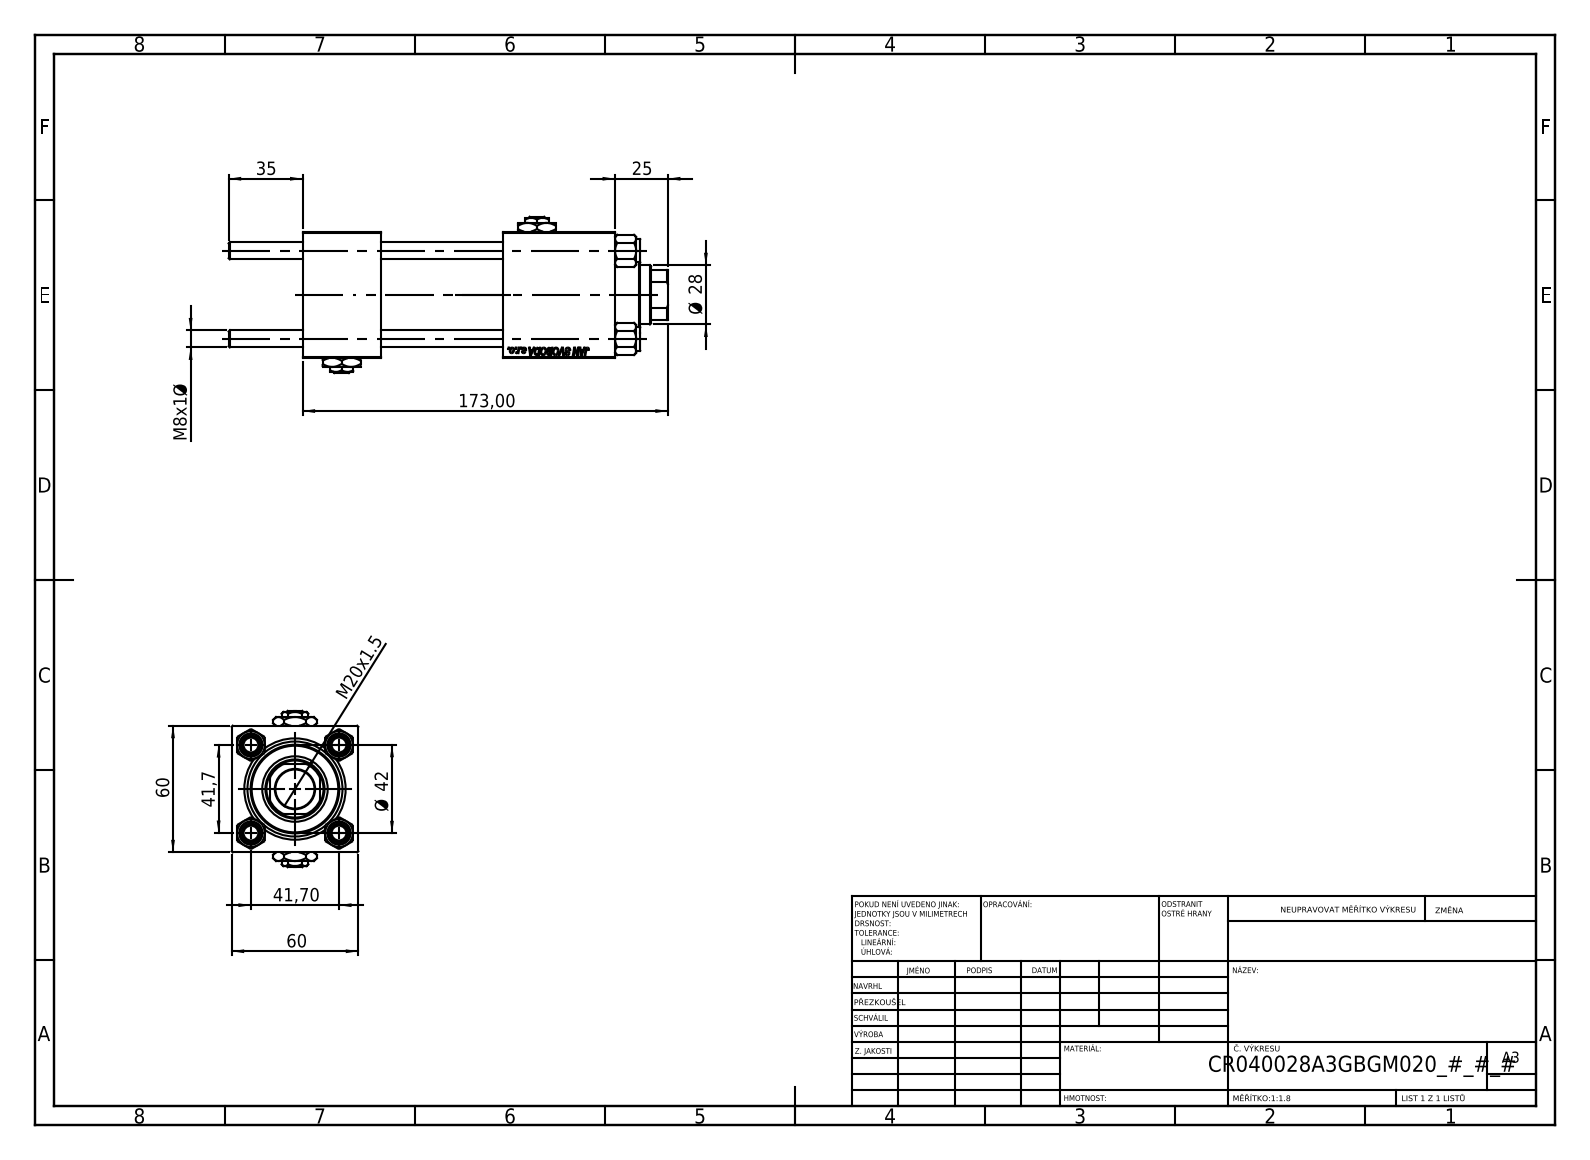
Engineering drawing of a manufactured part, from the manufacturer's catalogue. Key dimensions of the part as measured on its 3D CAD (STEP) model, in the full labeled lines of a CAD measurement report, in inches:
Part name (STEP PRODUCT): V215_VC_A; NUT_M5; V215CR_VCP; V215CR_BODY_A (+2 more)
STEP written by: SolidWorks 2019 (CONFIG_CONTROL_DESIGN)
Units: inches
Bodies: 13 solids, 1235 faces (569 planar, 88 cylindrical, 578 other)
Overall size (bounding box): 8.189 × 2.913 × 2.362
Volume: 26.38 in³ · Surface area: 190.7 in²
Round holes (diameter × count): ⌀0.315 ×4, ⌀0.276 ×2, ⌀0.656 ×2, ⌀0.945 ×2, ⌀0.728 ×1, ⌀1.102 ×1, ⌀1.22 ×1, ⌀1.575 ×1, ⌀1.772 ×1
Round bosses / shafts (diameter × count): ⌀0.433 ×4, ⌀1.811 ×1, ⌀1.654 ×1
Partial cylindrical surfaces — rounded edges, fillets, slot ends (radius × count): R0.531 ×1
Main face-to-face distances: 2.362, 1.457, 2.283, 3.74, 2.087, 5.827, 4.37, 4.697, 3.24, 0.957
Hole centre spacings: 1.161, 1.642, 2.322, 3.642
